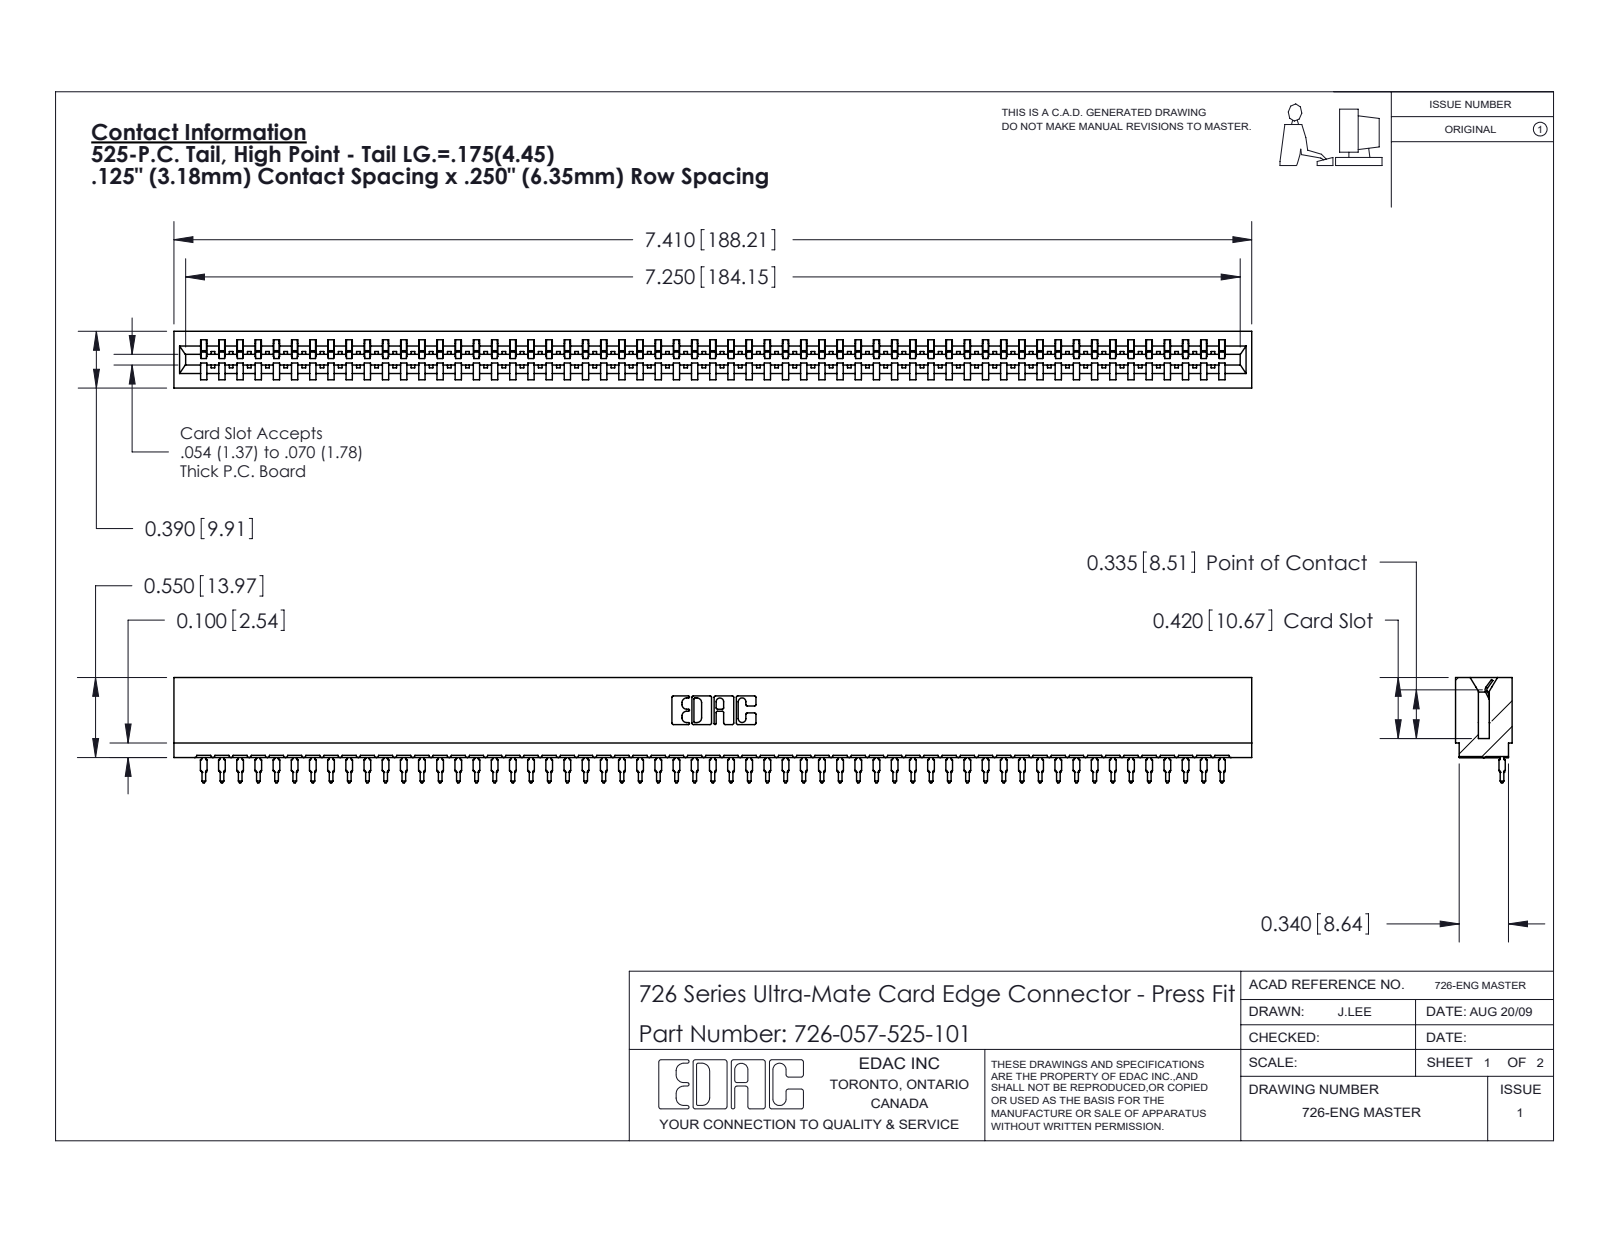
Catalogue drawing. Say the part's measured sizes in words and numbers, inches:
The part is named "726 Part_.515 Slot Depth - 01; 746-292-001_525; 726-057-525-101". Its 3-D file was written by "SolidWorks 2020 (CONFIG_CONTROL_DESIGN)". It is 58 solids with 6253 faces: 3646 planar, 1125 cylindrical and 1482 other. Overall it measures 7.41 by 0.724 by 0.39 inches. Its volume is 1.016 cubic inches and its surface area 39.31 square inches. Partial cylindrical surfaces (rounded edges, fillets, slot ends): 114 of radius 0.021, 58 of radius 0.015, 22 of radius 0.01, 6 of radius 0.007, 6 of radius 0.031, 4 of radius 0.005, 4 of radius 0.011, 3 of radius 0.026. The main face-to-face distances are 0.057, 0.333, 0.39, 0.025, 0.307, 0.25, 0.275, 0.365, 0.032, 0.174.
